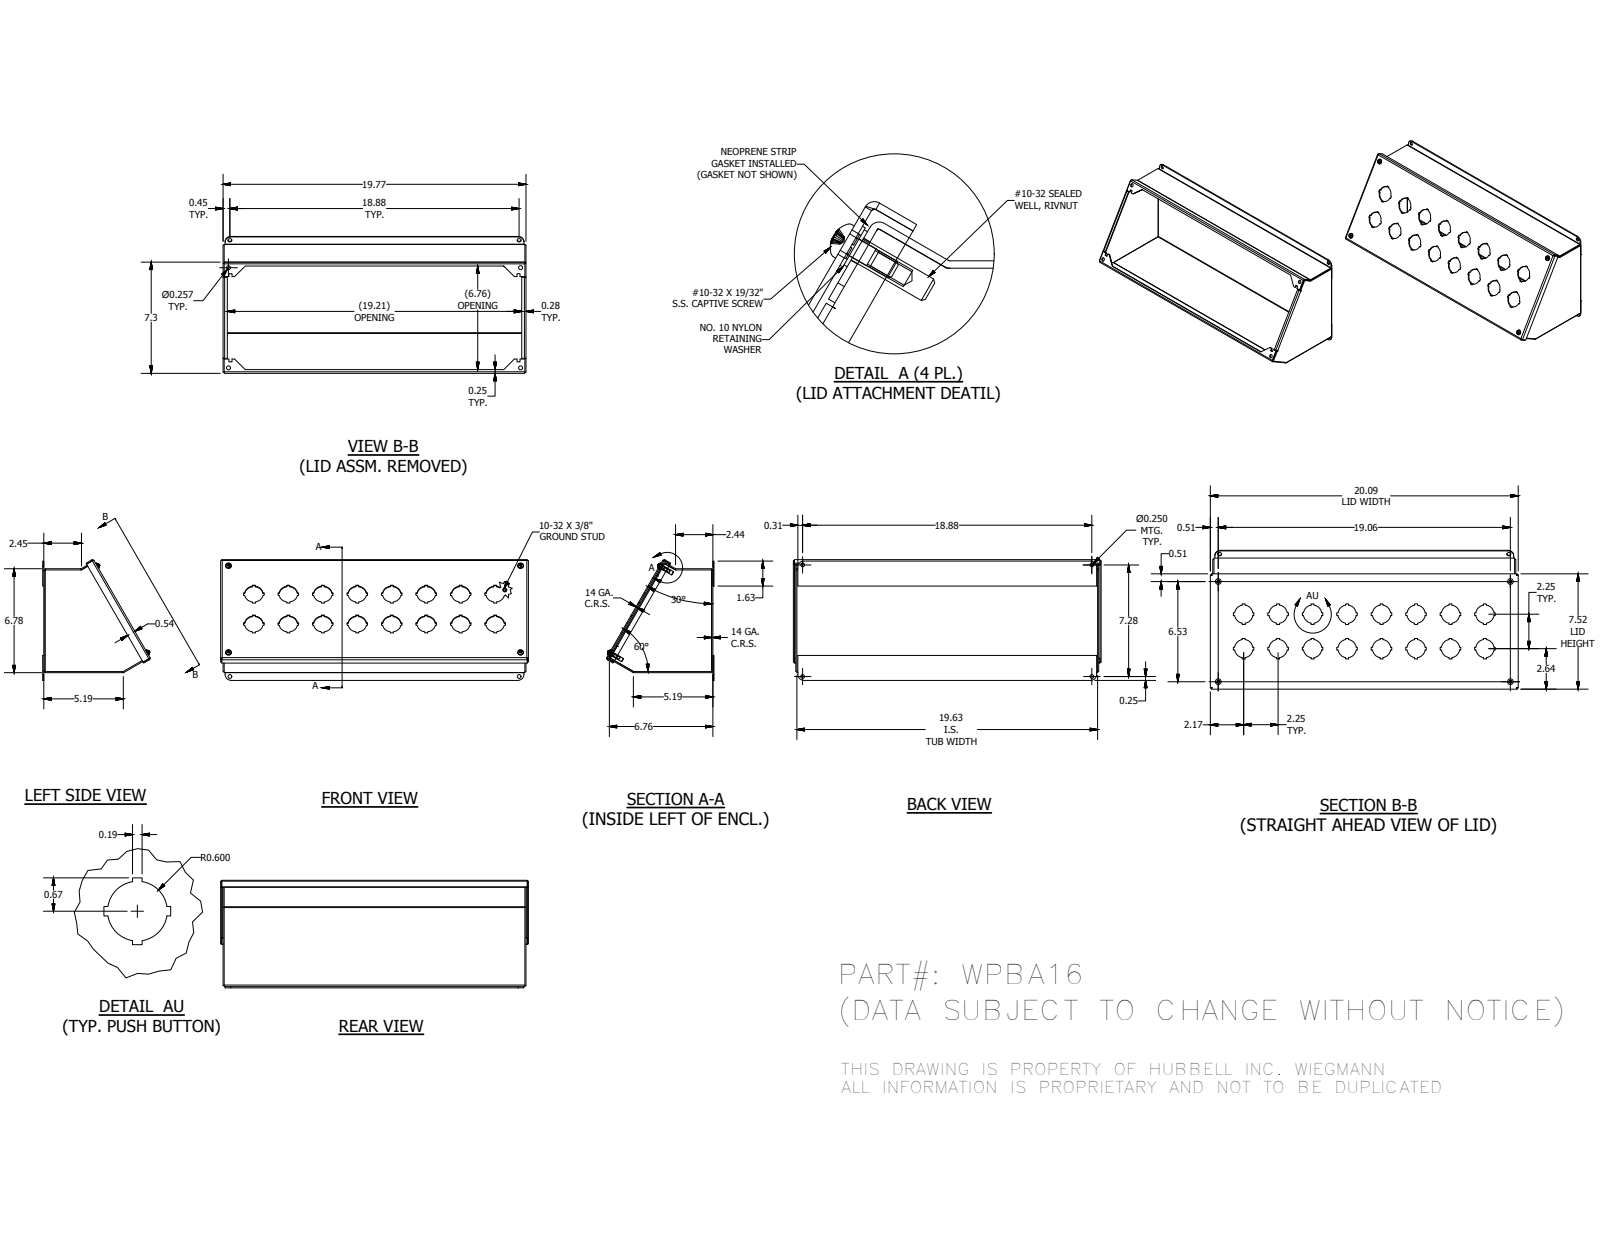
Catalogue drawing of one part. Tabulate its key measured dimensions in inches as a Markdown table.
| quantity | value |
| --- | --- |
| part name | WPBA16BKP; WPBA2ROWEWPR; WPBA2ROWEWPL; 34984 (+6 more) |
| STEP written by | Autodesk Inventor 2014 (AUTOMOTIVE_DESIGN) |
| units | inches |
| bodies | 19 solids, 736 faces (483 planar, 154 cylindrical, 99 other) |
| overall size | 20.087 × 7.873 × 7.016 |
| volume | 46.78 in³ |
| surface area | 1 293 in² |
| round holes (diameter × count) | 1.2 × 16, 0.156 × 4, 0.196 × 4, 0.25 × 4, 0.257 × 4, 0.278 × 4, 0.281 × 4 |
| round bosses / shafts (diameter × count) | 0.19 × 5, 0.453 × 4, 0.406 × 4, 0.373 × 4, 0.248 × 4, 0.25 × 1 |
| partial cylindrical surfaces (radius × count) | 0.031 × 12, 0.105 × 12, 0.089 × 4, 0.375 × 4 |
| main face-to-face distances | 0.074, 6.706, 0.148, 0.074, 6.632, 6.78, 19.699, 19.699, 19.773, 19.625 |
| hole center spacings | 2.25, 3.182, 4.5, 5.031, 6.75, 7.115, 2.25, 9 |
